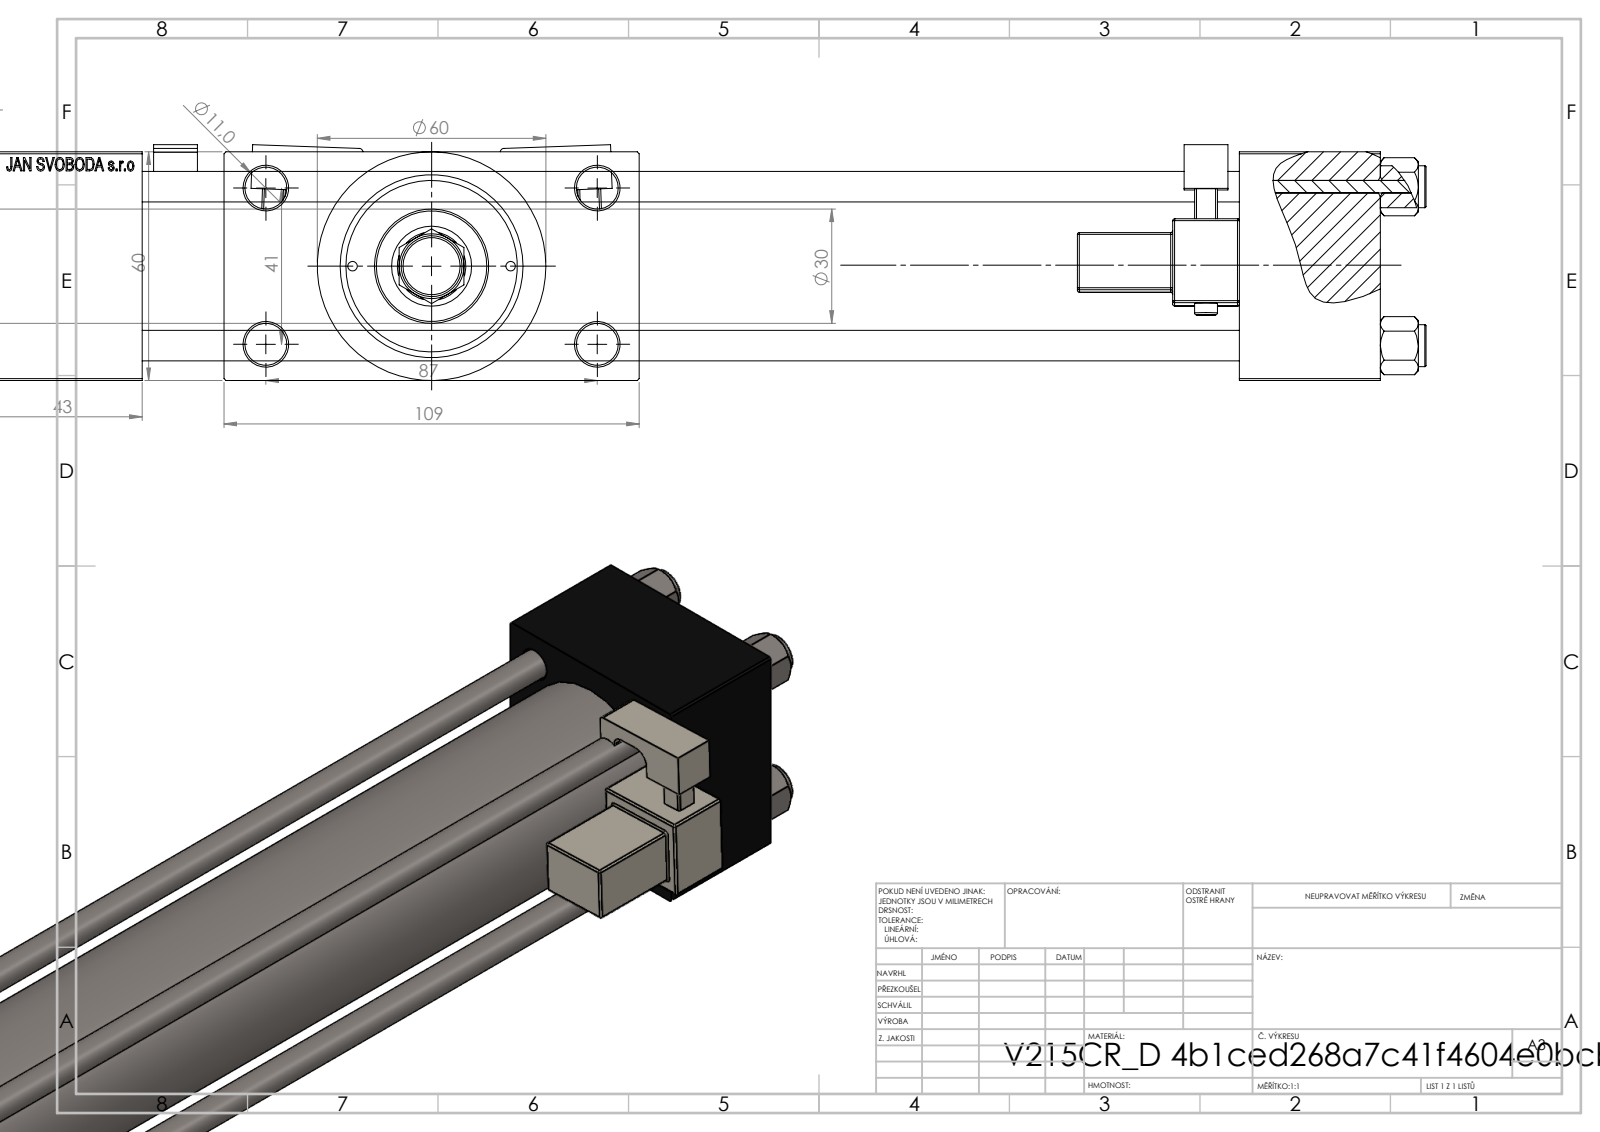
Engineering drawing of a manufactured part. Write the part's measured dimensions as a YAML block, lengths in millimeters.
part_name: "NUT_M5_D; V215CR_D_Body; V215CR_VCP_D; V215CR_D_TYCINKA (+3 more)"
step_written_by: "SolidWorks 2019 (CONFIG_CONTROL_DESIGN)"
units: millimeters
bodies: {solids: 14, faces: 1318, planar: 574, cylindrical: 156, other: 588}
overall_size: [443, 109, 61.9]
volume: 756556
surface_area: 234925
round_holes:
  - {diameter: 8, count: 4}
  - {diameter: 11, count: 4}
  - {diameter: 2.5, count: 2}
  - {diameter: 7, count: 2}
  - {diameter: 16.66, count: 2}
  - {diameter: 24, count: 2}
  - {diameter: 8.5, count: 1}
  - {diameter: 18, count: 1}
  - {diameter: 21, count: 1}
  - {diameter: 31, count: 1}
  - {diameter: 40, count: 1}
  - {diameter: 45, count: 1}
round_bosses_or_shafts:
  - {diameter: 11, count: 4}
  - {diameter: 6, count: 2}
  - {diameter: 60, count: 1}
  - {diameter: 46, count: 1}
  - {diameter: 30, count: 1}
  - {diameter: 16, count: 1}
  - {diameter: 10, count: 1}
partial_cylinders:
  - {radius: 0.5, count: 48}
  - {radius: 1, count: 2}
  - {radius: 2.5, count: 2}
  - {radius: 4, count: 2}
  - {radius: 8.5, count: 1}
face_to_face_distances: [60, 288, 24.5, 84.5, 37, 325, 368, 331, 43, 109]
hole_center_spacings: [20.85, 22.65, 29.49, 30.62, 41.7, 46.53, 47.15, 48.09]
